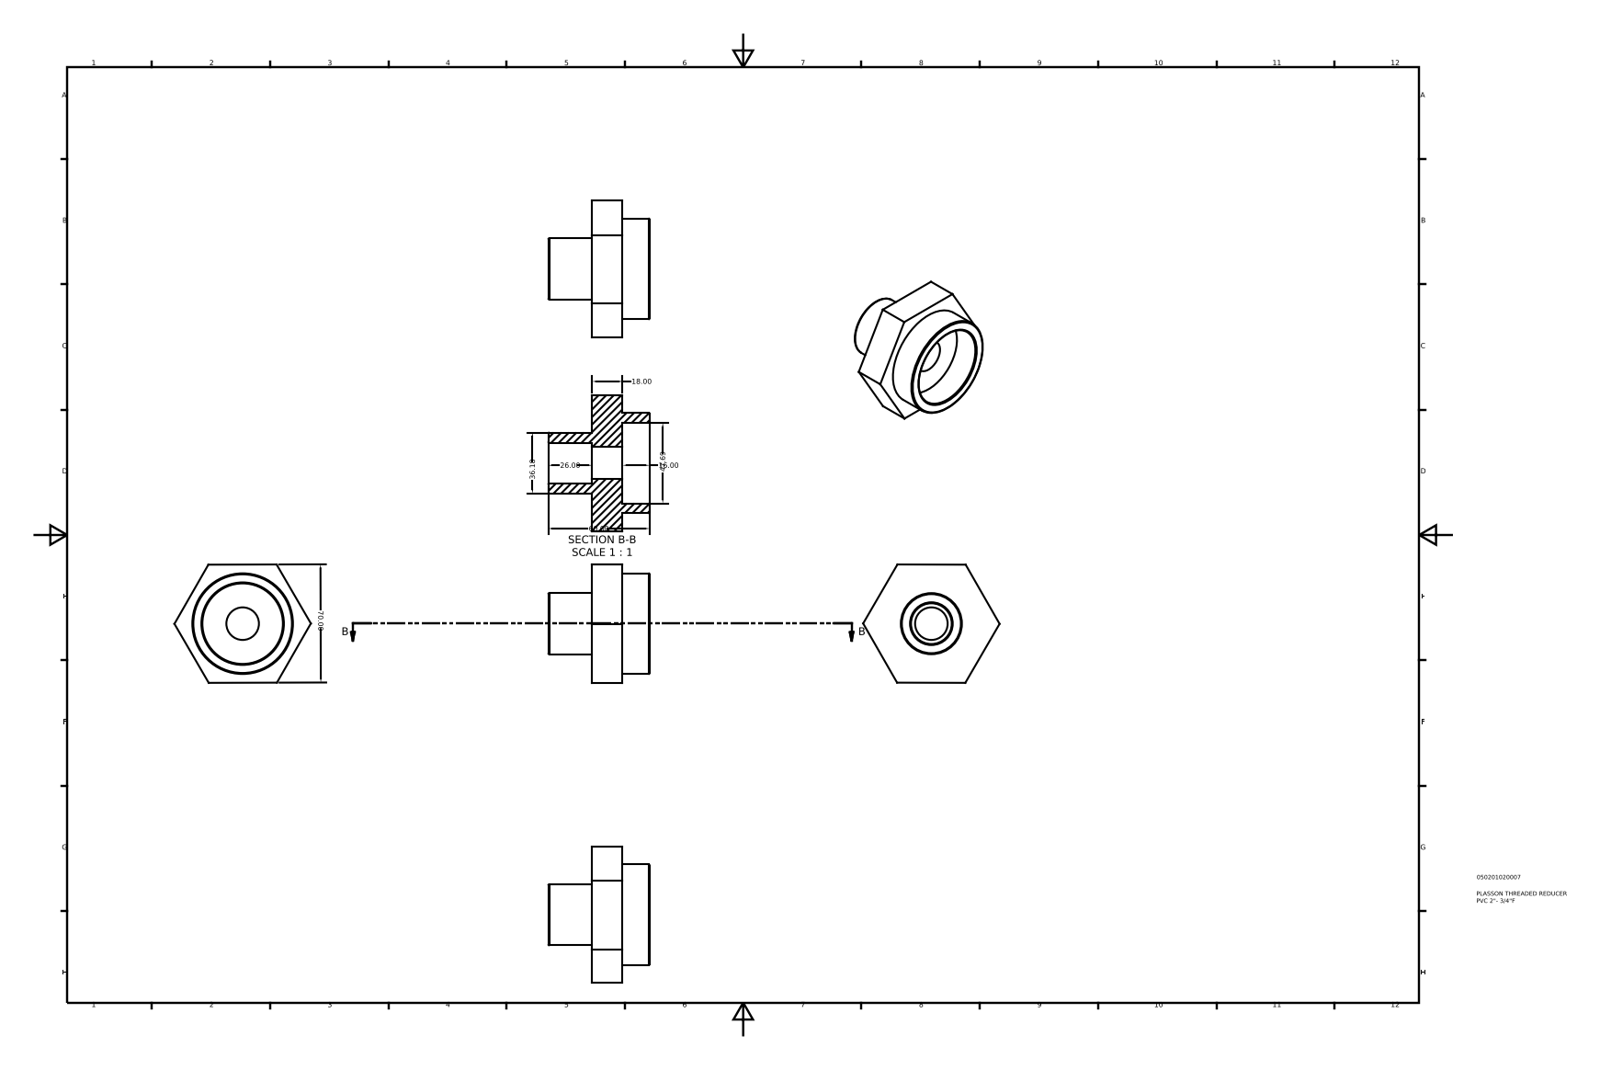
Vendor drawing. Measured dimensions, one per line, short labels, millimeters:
name: 050201020007
written by: Autodesk Inventor 2015 (AUTOMOTIVE_DESIGN)
unit: mm
bodies: 1 solid, 21 faces (12 planar, 5 cylindrical, 4 other)
size: 80.83 × 70.12 × 60
volume: 102 004 mm³; area: 23 542 mm²
holes: 1× ⌀19.29, 1× ⌀24.12, 1× ⌀47.69
bosses: 1× ⌀59.61, 1× ⌀36.18
face distances: 18, 70.04, 34, 16, 70, 26, 44, 60
